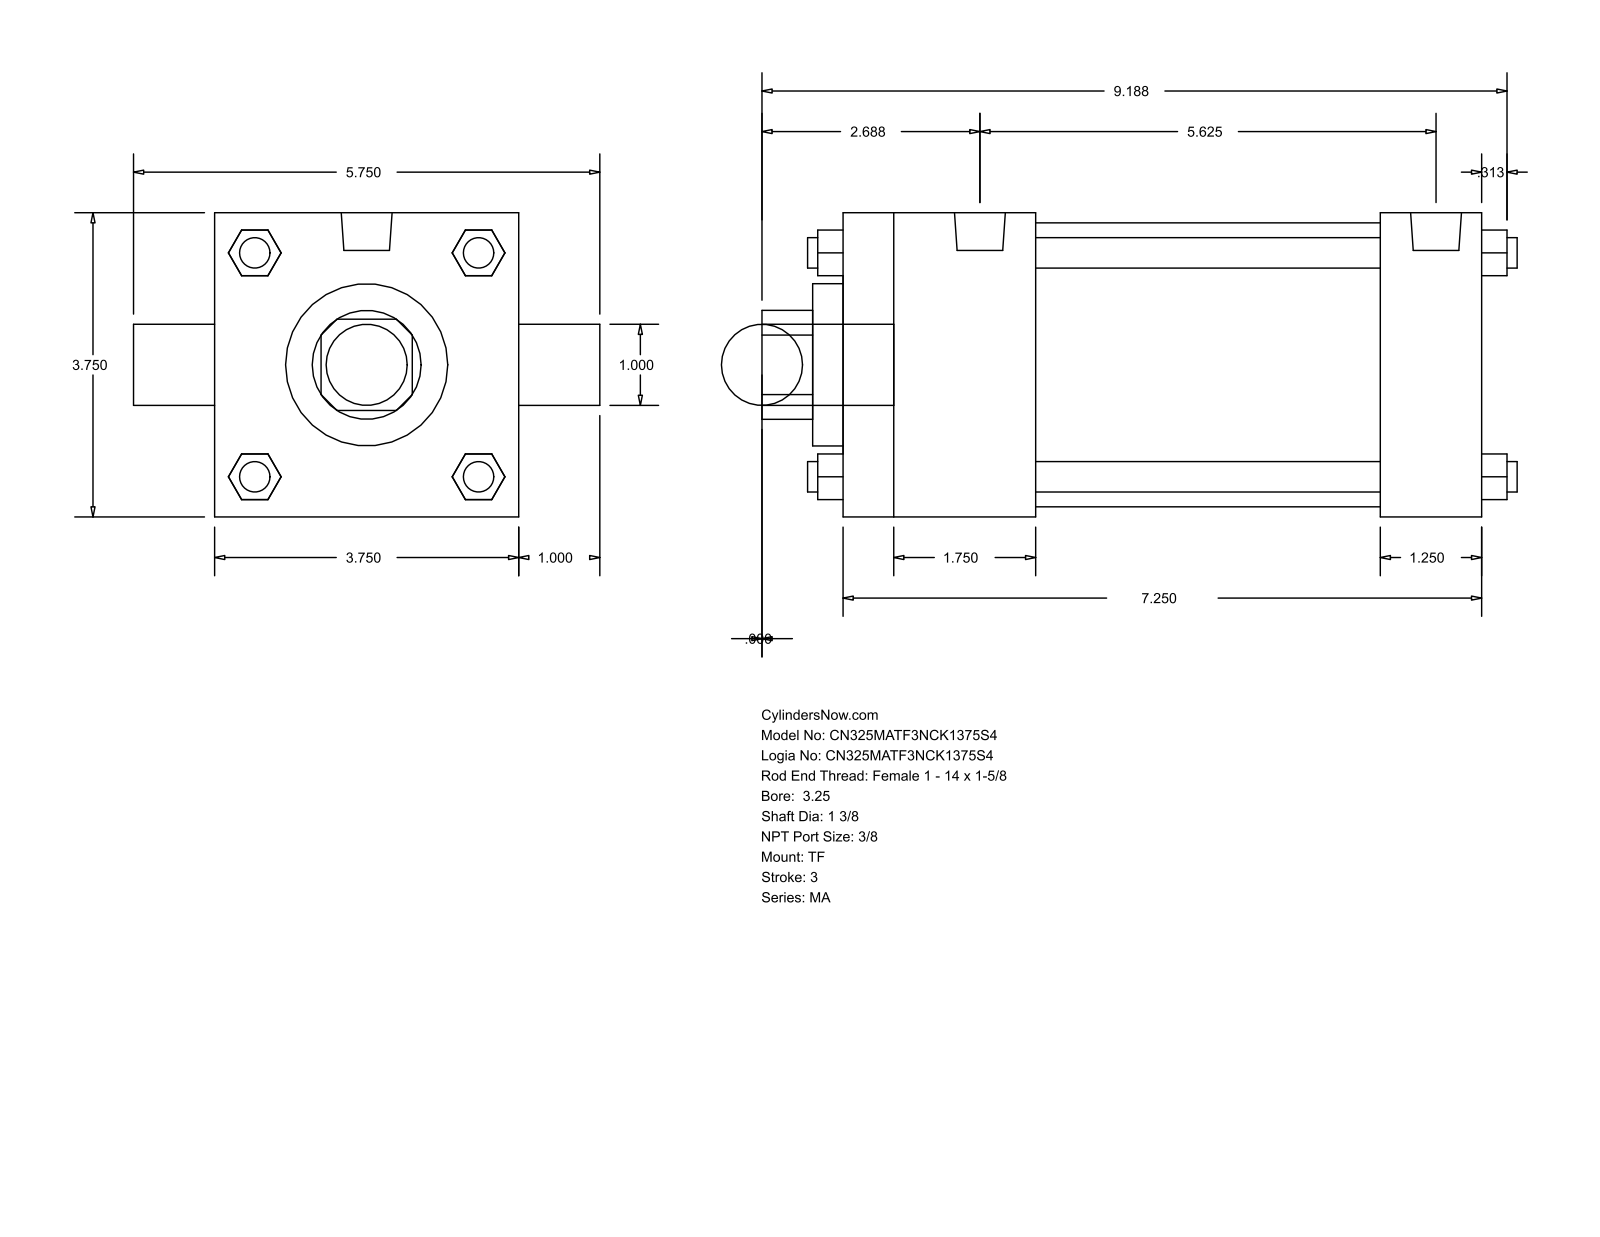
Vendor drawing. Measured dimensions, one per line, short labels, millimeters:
name: MA_TF__0325_1.375
written by: GSSL Pune (CONFIG_CONTROL_DESIGN)
unit: mm
bodies: 0 solids, 120 faces (92 planar, 28 cylindrical, 0 other)
size: 236.54 × 146.05 × 95.25
holes: 1× ⌀25.4, 1× ⌀34.92, 1× ⌀50.8, 1× ⌀88.9
bosses: 4× ⌀9.53, 3× ⌀11.11, 2× ⌀15.93, 1× ⌀25.4
rounds: 1× R17.06
face distances: 95.24, 200.03, 60.32, 168.28, 107.96, 139.71, 31.75, 9.52, 69.84, 177.8
